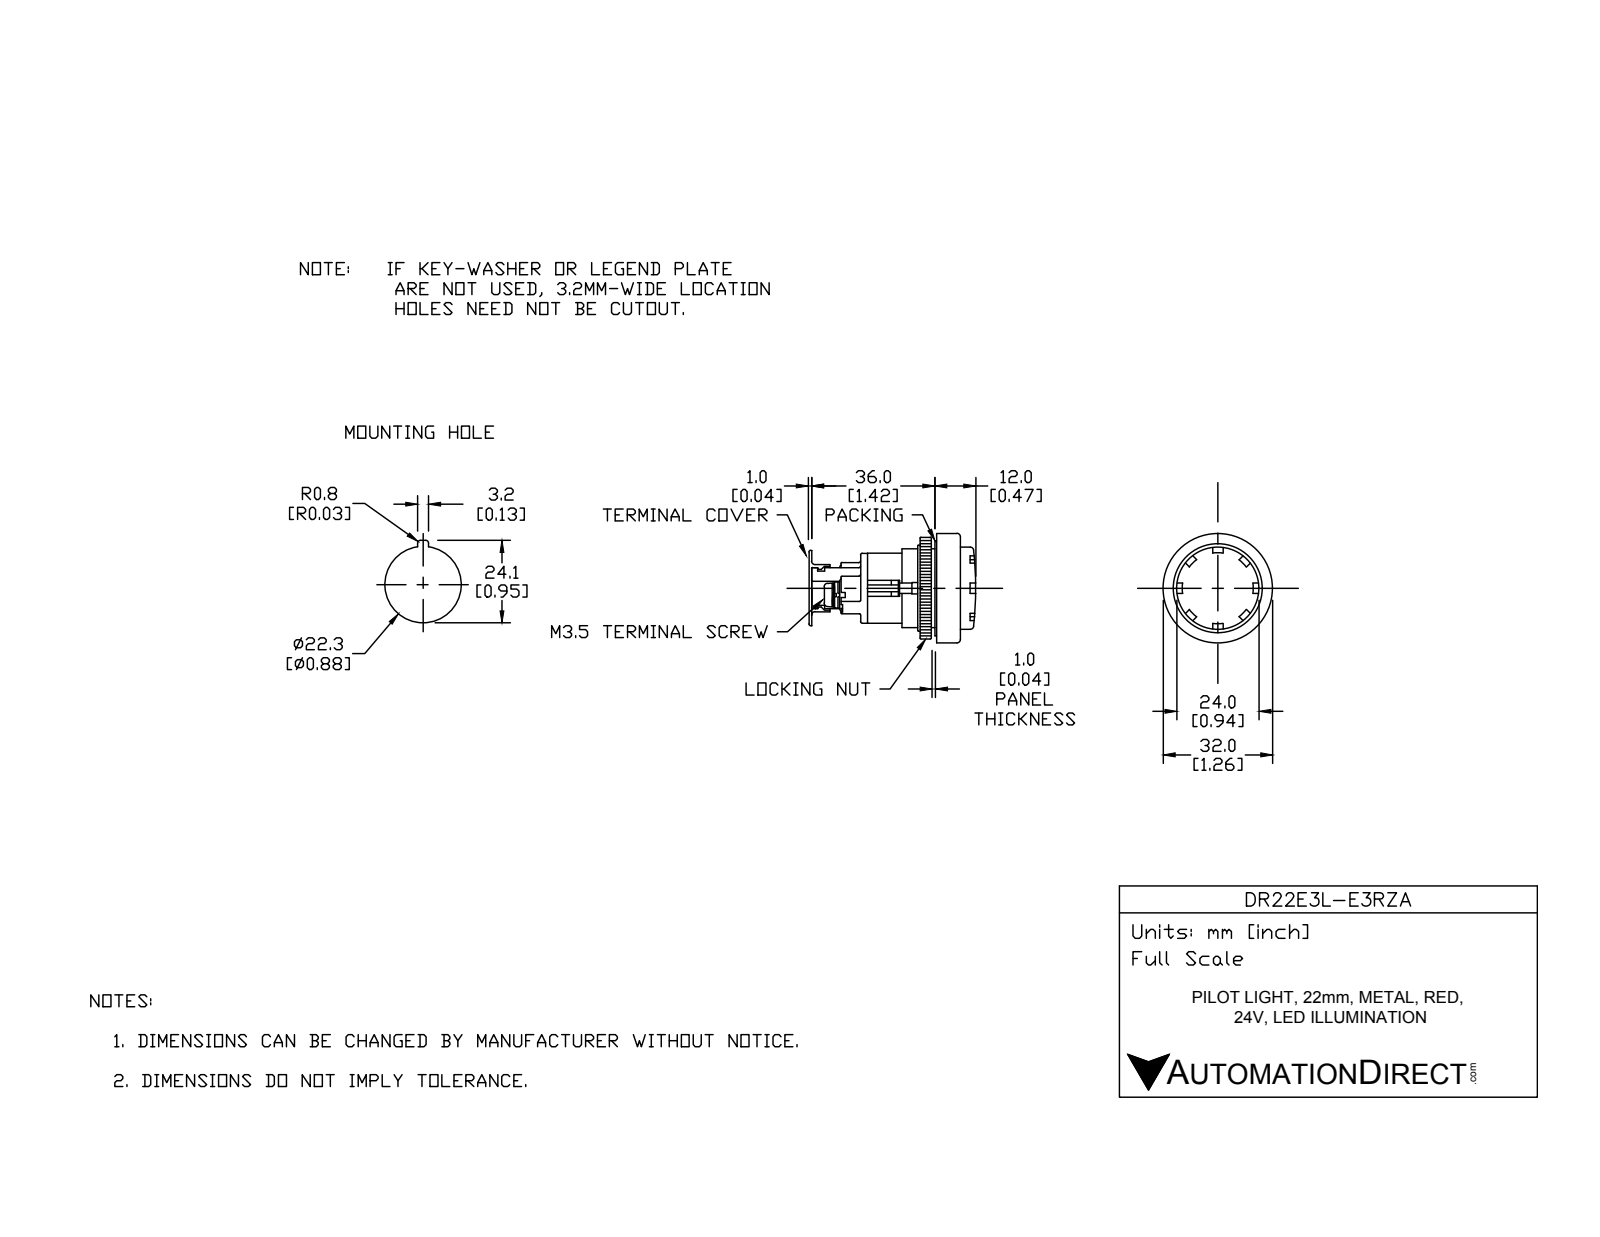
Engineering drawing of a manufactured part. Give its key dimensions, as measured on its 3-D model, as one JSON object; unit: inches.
{"part_name": "DR22E3L-E3RZA", "step_written_by": "SolidWorks 2017 (AUTOMOTIVE_DESIGN)", "units": "inches", "bodies": {"solids": 11, "faces": 126, "planar": 76, "cylindrical": 38, "other": 12}, "overall_size": [1.89, 1.26, 1.26], "volume_in3": 1.188, "surface_area_in2": 17.73, "round_holes": [[0.252, 2], [0.866, 1], [0.984, 1], [1.181, 1]], "round_bosses_or_shafts": [[0.228, 2], [1.26, 1], [1.169, 1], [1.161, 1], [1.063, 1], [0.858, 1]], "partial_cylinders_radius": [[0.02, 8]], "face_to_face_distances": [0.157, 1.024, 0.236, 0.63, 0.039, 0.787, 1.063, 1.654, 0.591, 0.433], "hole_center_spacings": [0.238, 0.476]}
